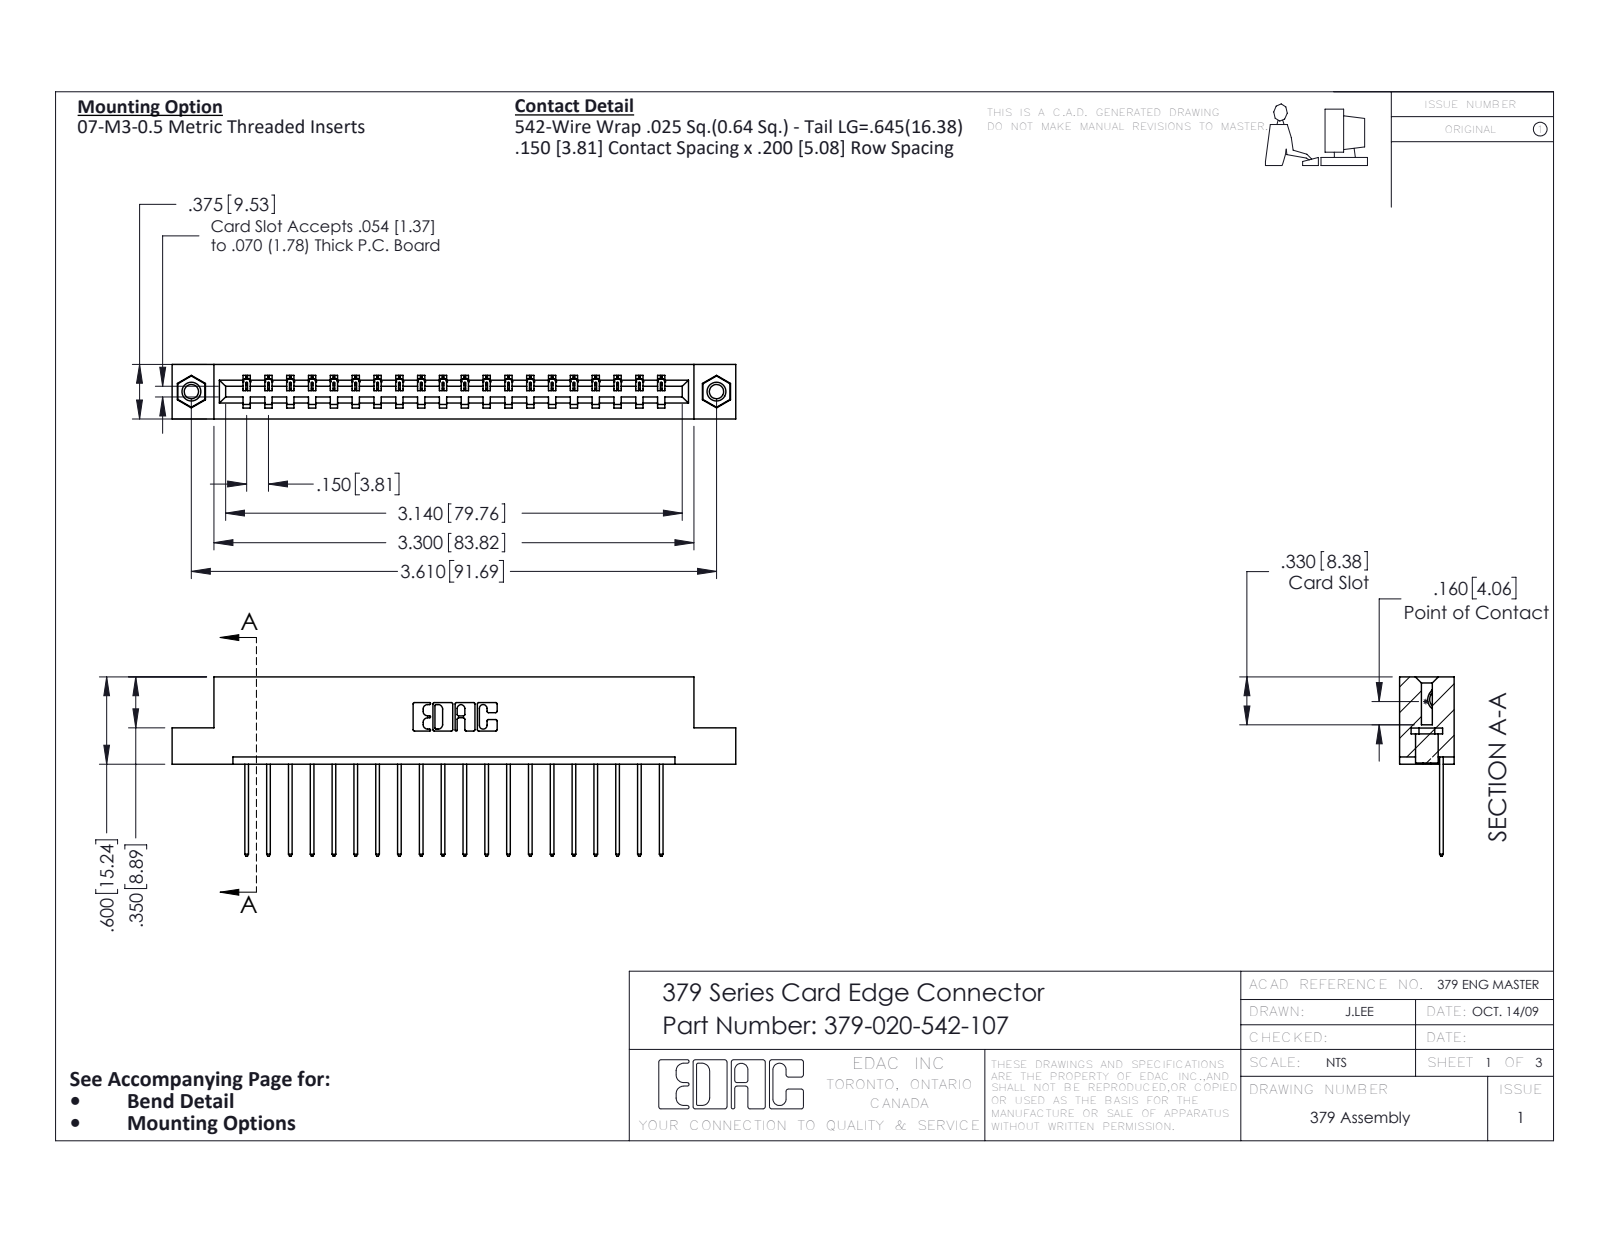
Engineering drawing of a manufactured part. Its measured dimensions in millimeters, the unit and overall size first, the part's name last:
Units: millimetres
Overall size (bounding box): 98.4 × 31.3 × 9.5
Round holes (diameter × count): ⌀2.5 ×2, ⌀3.2 ×2, ⌀4 ×2
Round bosses / shafts (diameter × count): ⌀3.9 ×2
Partial cylindrical surfaces — rounded edges, fillets, slot ends (radius × count): R0.2 ×40, R0.3 ×40, R0.3 ×22, R0.2 ×6, R0.8 ×6, R0.7 ×3, R0.4 ×1, R0.6 ×1
Main face-to-face distances: 7.6, 1.9, 9.5, 15.2, 5.7, 3.8, 7, 5.1, 2.5, 0.6
Hole centre spacings: 91.7
Volume: 10 100 mm³ · Surface area: 10 570 mm²
Bodies: 23 solids, 1334 faces (942 planar, 376 cylindrical, 16 other)
Part name (STEP PRODUCT): 379 Part_Flush - .156 Dia - TI; 345-250-001_345-250-005-103; 379-020-542-107; 345-292-001_345-293-142
STEP written by: SolidWorks 2016 (CONFIG_CONTROL_DESIGN)
